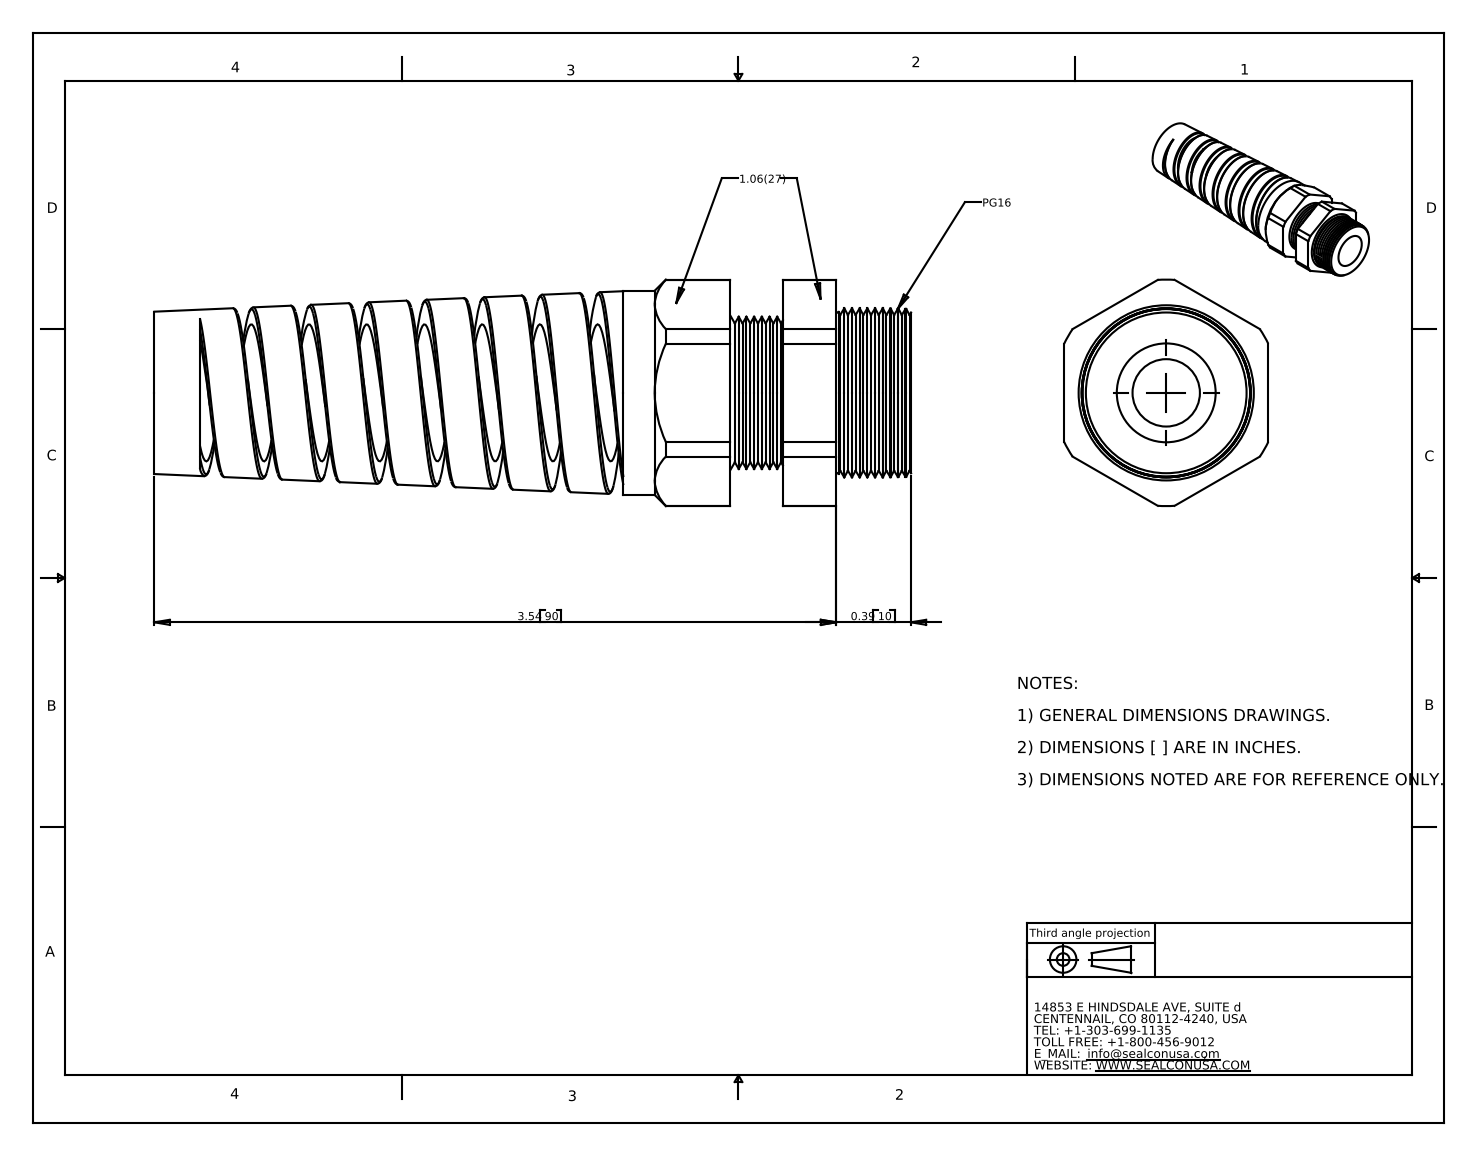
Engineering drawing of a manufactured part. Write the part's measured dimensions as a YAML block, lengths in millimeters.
part_name: "CF16BR-BK"
step_written_by: "SolidWorks 2007 (CONFIG_CONTROL_DESIGN)"
units: millimeters
bodies: {solids: 2, faces: 176, planar: 24, cylindrical: 39, other: 113}
overall_size: [99.8, 29.9, 26.9]
volume: 24220
surface_area: 17750
round_holes:
  - {diameter: 8.9, count: 1}
  - {diameter: 18.1, count: 1}
  - {diameter: 20.3, count: 1}
round_bosses_or_shafts:
  - {diameter: 26.9, count: 1}
partial_cylinders:
  - {radius: 9.3, count: 1}
  - {radius: 14.9, count: 1}
face_to_face_distances: [26.9, 6.9, 23.8, 16.9, 13.9, 7, 9.9, 12.2, 19.2, 26.2]
